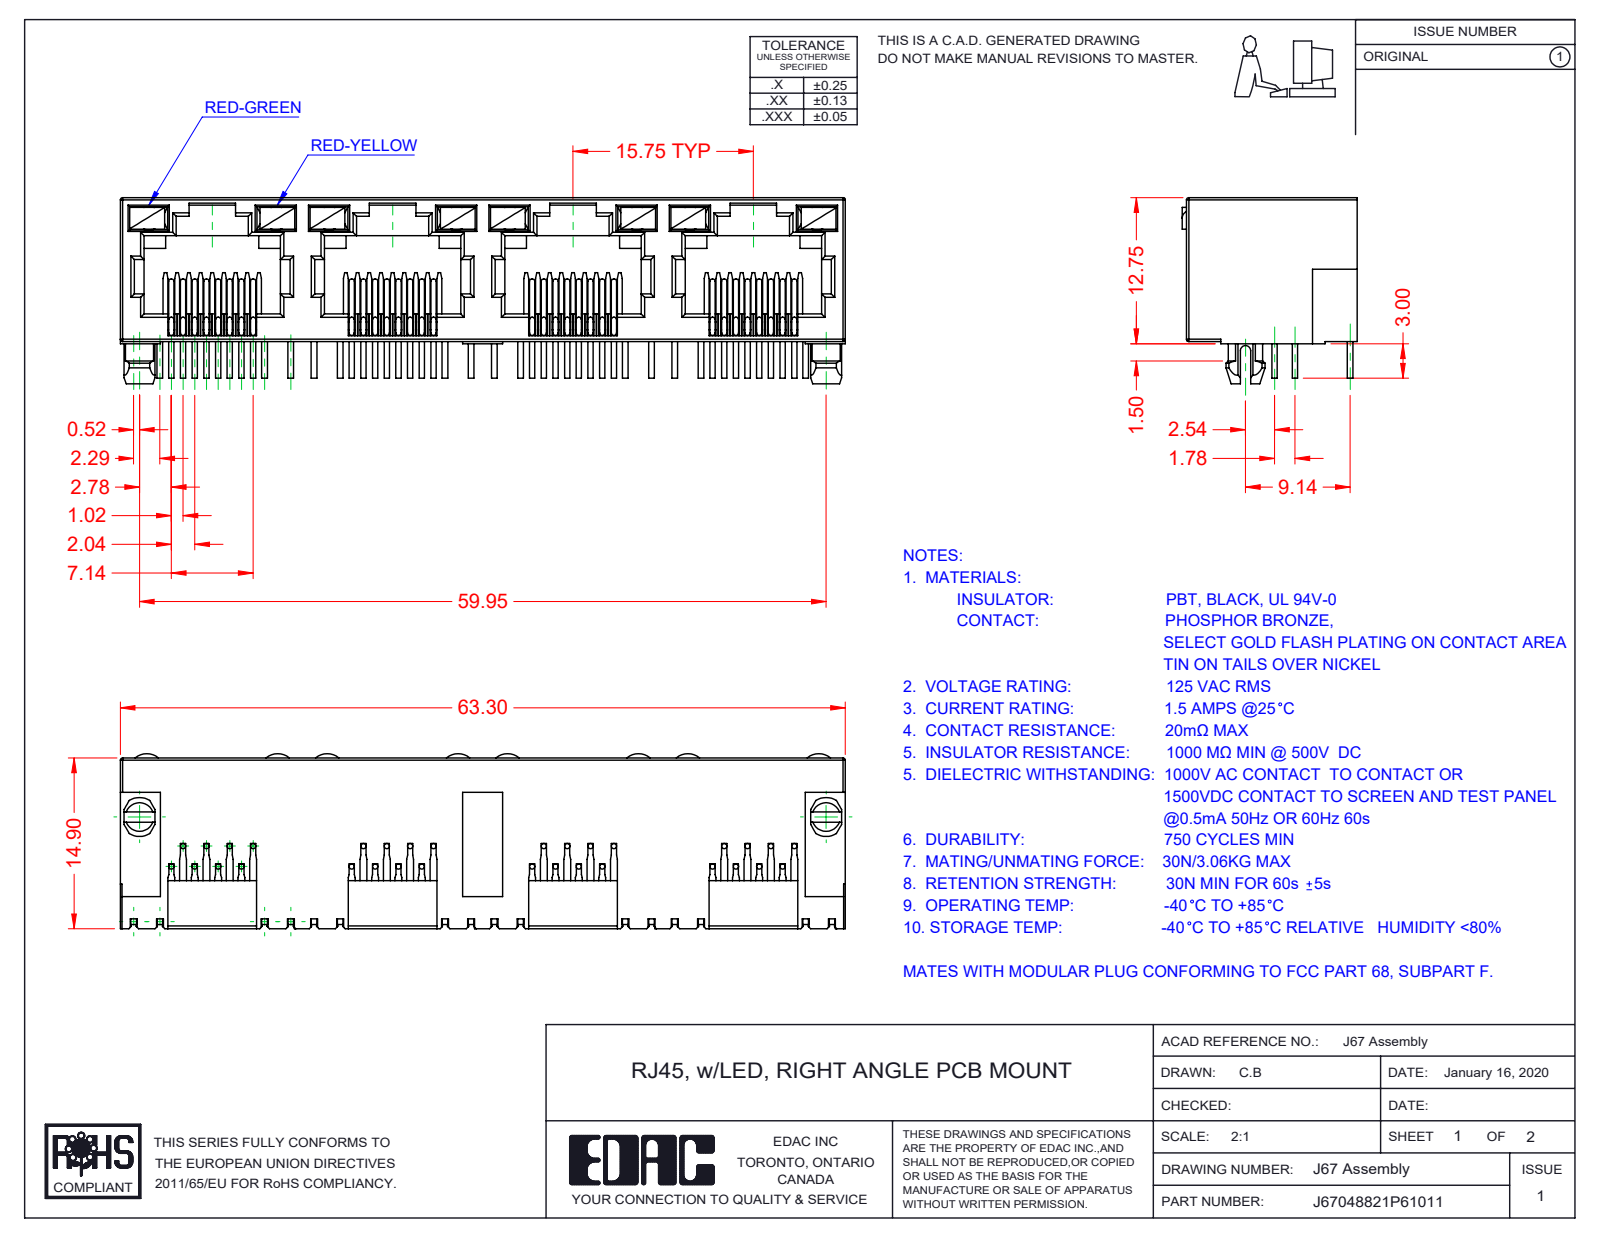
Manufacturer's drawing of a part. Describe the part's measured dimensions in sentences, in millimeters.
The part is named "J67048822P68011; 67 Insulator; 67 LED LH_6-Red-Green; 67 LED RH_8-Red-Yellow (+1 more)". Its 3-D file was written by "SolidWorks 2016 (CONFIG_CONTROL_DESIGN)". It is 41 solids with 2481 faces: 1781 planar, 492 cylindrical and 208 other. Overall it measures 63.3 by 16.25 by 15.28 millimeters. Its volume is 5 159 cubic millimeters and its surface area 11 573 square millimeters. Round bosses or shafts: 96 of diameter 0.46. Partial cylindrical surfaces (rounded edges, fillets, slot ends): 66 of radius 0.2, 29 of radius 0.3, 9 of radius 0.45, 8 of radius 1.55, 2 of radius 1.5, 2 of radius 1.7, 1 of radius 0.35, 1 of radius 1. The main face-to-face distances are 0.5, 12.55, 1.89, 0.89, 10, 15.75, 1, 1.39, 11, 11.89.
